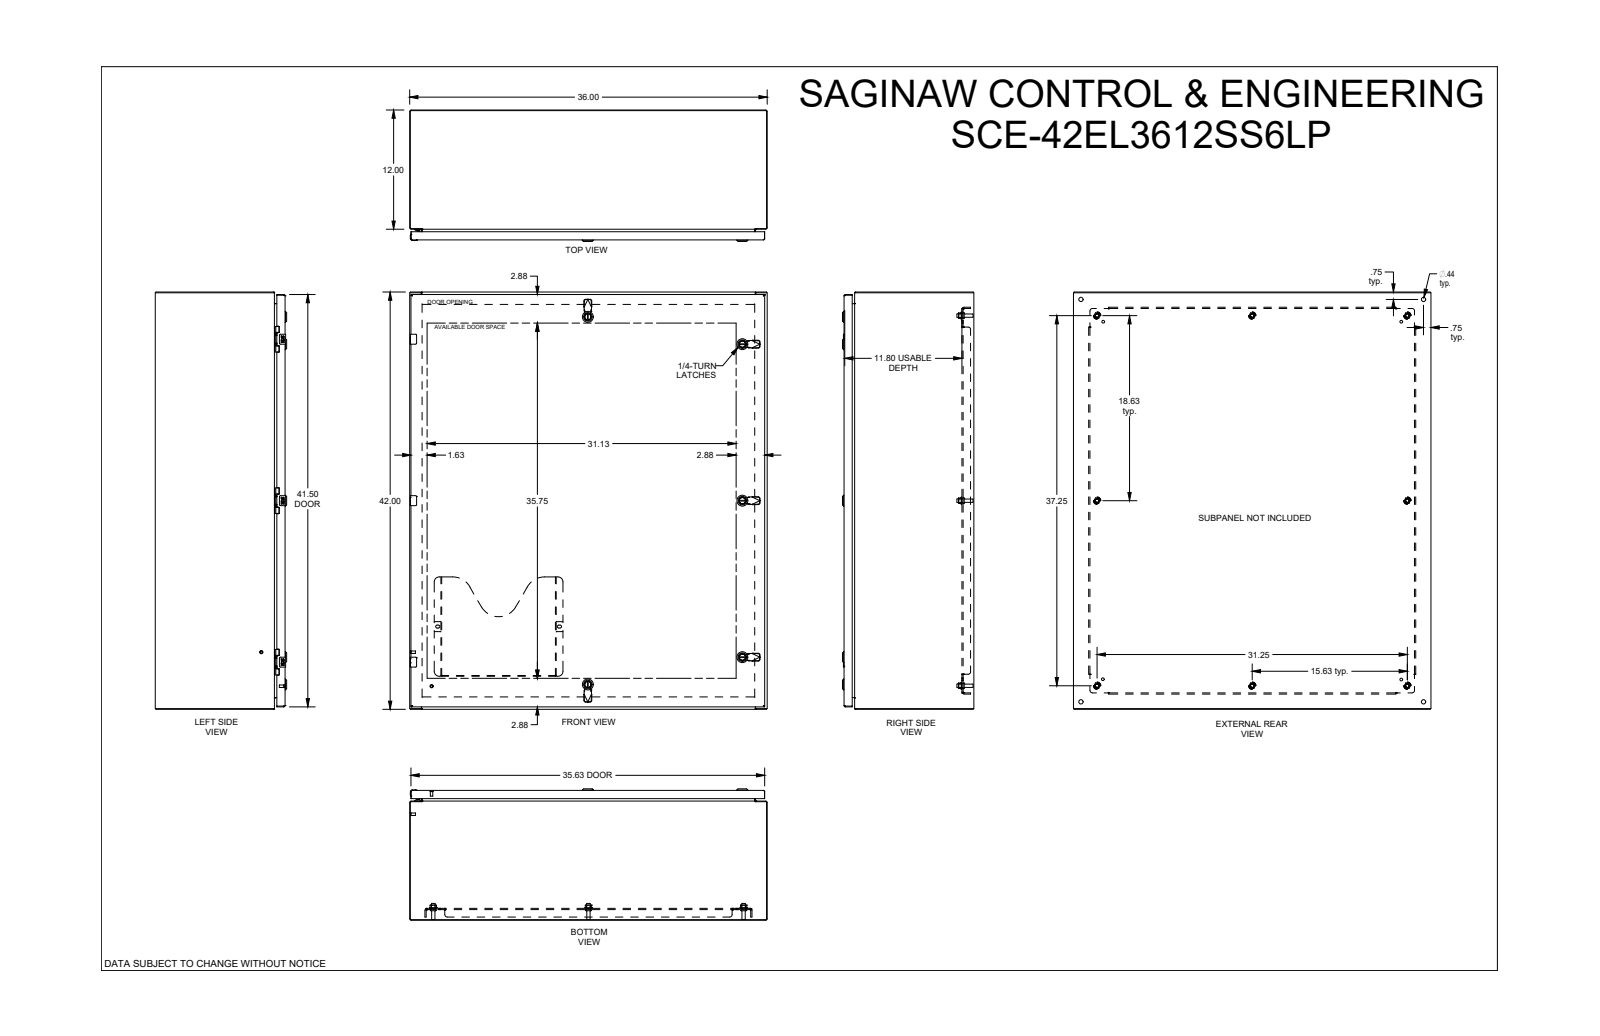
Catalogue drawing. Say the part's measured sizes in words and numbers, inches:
The part is named "SCE-42EL3612SS6LP". Its 3-D file was written by "SolidWorks 2019 (CONFIG_CONTROL_DESIGN)". It is 0 solids with 4758 faces: 2318 planar, 1321 cylindrical and 1119 other. Overall it measures 42 by 36 by 13.23 inches. Round holes: 8 of diameter 0.367, 8 of diameter 0.5, 6 of diameter 0.172, 6 of diameter 0.205, 6 of diameter 0.244, 6 of diameter 0.266, 5 of diameter 0.197, 5 of diameter 0.315, 5 of diameter 0.394, 5 of diameter 0.634, 4 of diameter 0.281, 4 of diameter 0.375. Round bosses or shafts: 9 of diameter 0.17, 8 of diameter 0.366, 8 of diameter 0.332, 6 of diameter 0.25, 5 of diameter 1.102, 5 of diameter 0.866, 5 of diameter 0.802, 5 of diameter 0.78. Partial cylindrical surfaces (rounded edges, fillets, slot ends): 142 of radius 0.012, 52 of radius 0.01, 52 of radius 0.02, 36 of radius 0.015, 23 of radius 0.04, 20 of radius 0.157, 14 of radius 0.07, 13 of radius 0.03. The main face-to-face distances are 0.075, 0.075, 12.923, 12.998, 13.073, 12.998, 1.2, 11.873, 1, 1.125. The hole center spacings are 16.25, 0.985, 32.5, 0.02, 4.493, 15.265, 16.25, 16.25.
